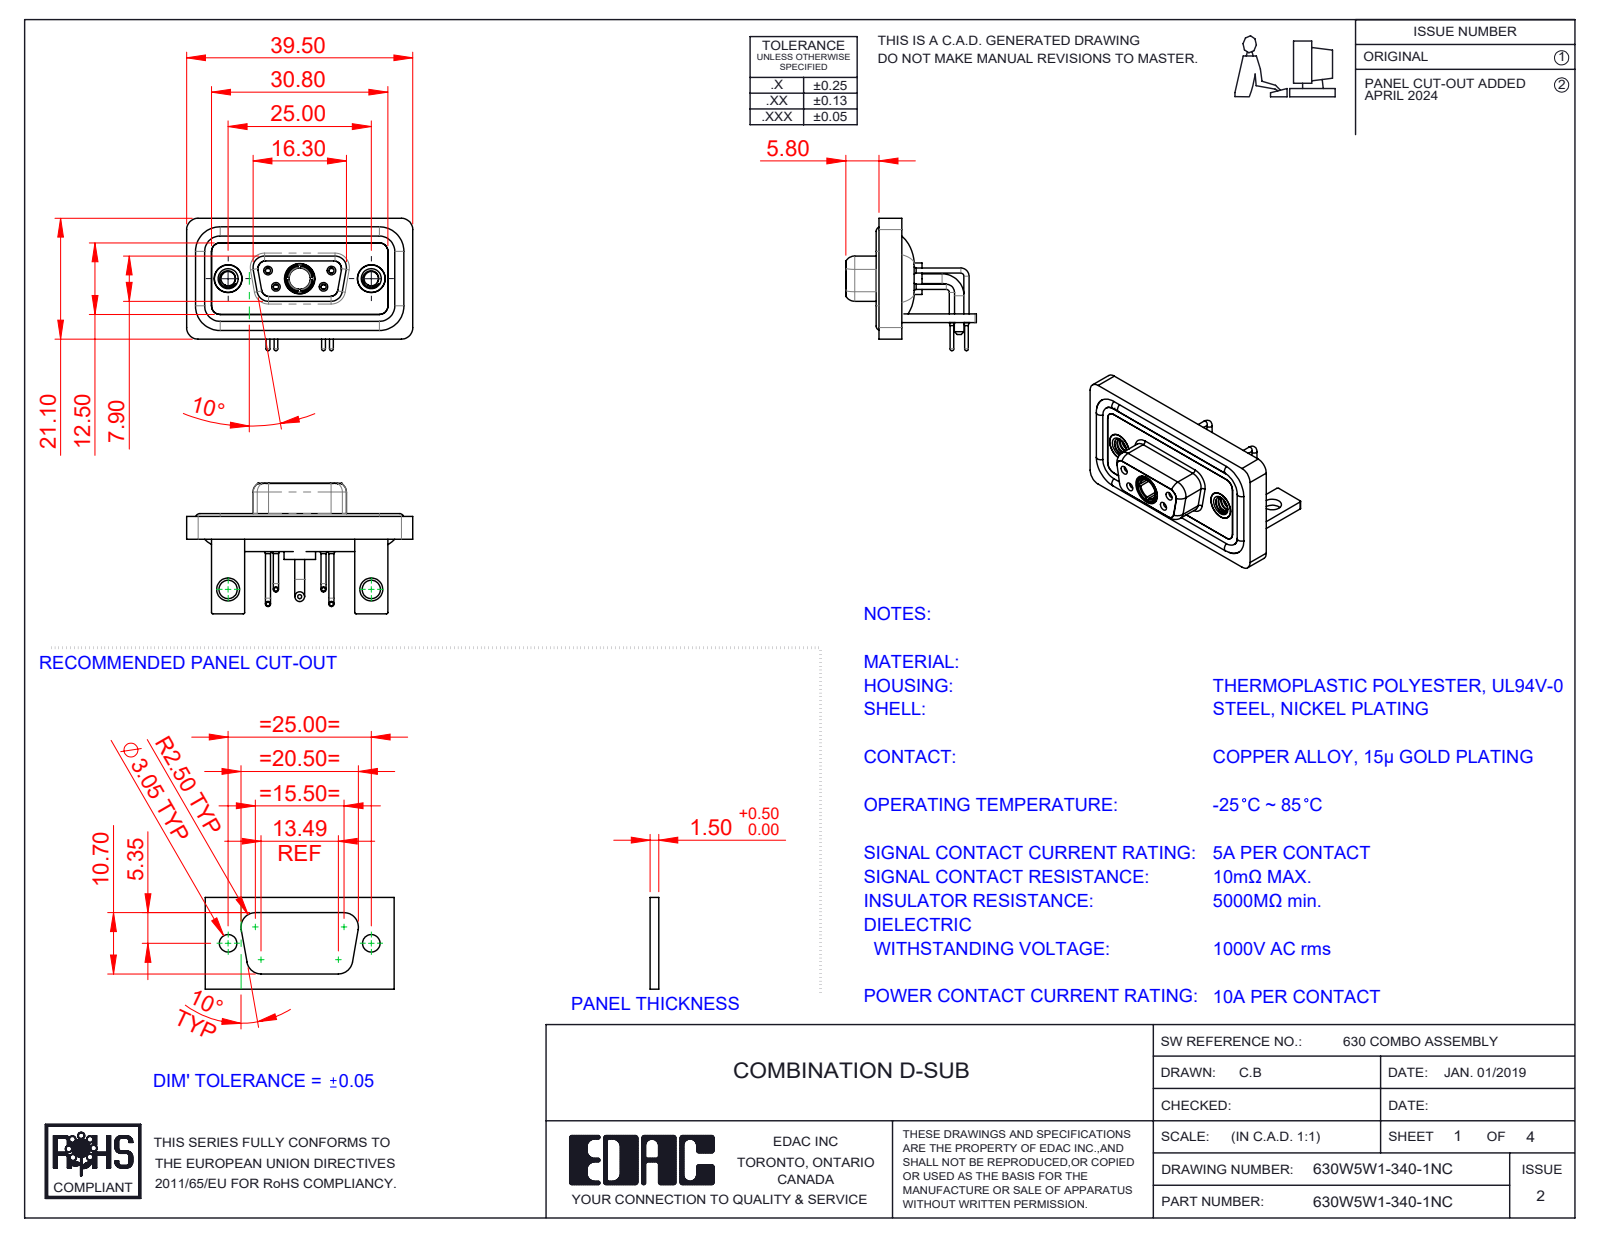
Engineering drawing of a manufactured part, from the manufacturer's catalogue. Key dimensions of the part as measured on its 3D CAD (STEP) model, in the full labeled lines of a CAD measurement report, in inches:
Part name (STEP PRODUCT): 630Combo Housing_5W1; 630Combo Threaded Rivet_A; 630Combo Contact Row 2_50 Contacts; 630Combo Shell Front_09 Contacts (+6 more)
STEP written by: SolidWorks 2023 (CONFIG_CONTROL_DESIGN)
Units: inches
Bodies: 15 solids, 718 faces (214 planar, 327 cylindrical, 177 other)
Overall size (bounding box): 1.555 × 0.91 × 0.898
Volume: 0.313 in³ · Surface area: 13.22 in²
Round holes (diameter × count): ⌀0.035 ×4, ⌀0.043 ×4, ⌀0.059 ×4, ⌀0.079 ×4, ⌀0.191 ×3, ⌀0.063 ×2, ⌀0.067 ×2, ⌀0.098 ×2, ⌀0.126 ×2, ⌀0.157 ×2, ⌀0.159 ×2, ⌀0.197 ×2
Round bosses / shafts (diameter × count): ⌀0.063 ×6, ⌀0.035 ×4, ⌀0.026 ×4, ⌀0.195 ×2, ⌀0.189 ×2, ⌀0.067 ×2, ⌀0.217 ×1, ⌀0.205 ×1
Partial cylindrical surfaces — rounded edges, fillets, slot ends (radius × count): R0.079 ×19, R0.059 ×18, R0.01 ×16, R0.053 ×8, R0.063 ×8, R0.02 ×5, R0.024 ×4, R0.026 ×4
Main face-to-face distances: 0.016, 0.114, 0.059, 0.071, 0.043, 0.146, 0.063, 0.031, 0.098, 0.122
Hole centre spacings: 0.124, 0.225, 0.28, 0.492, 0.713, 0.984, 0.173, 0.173
